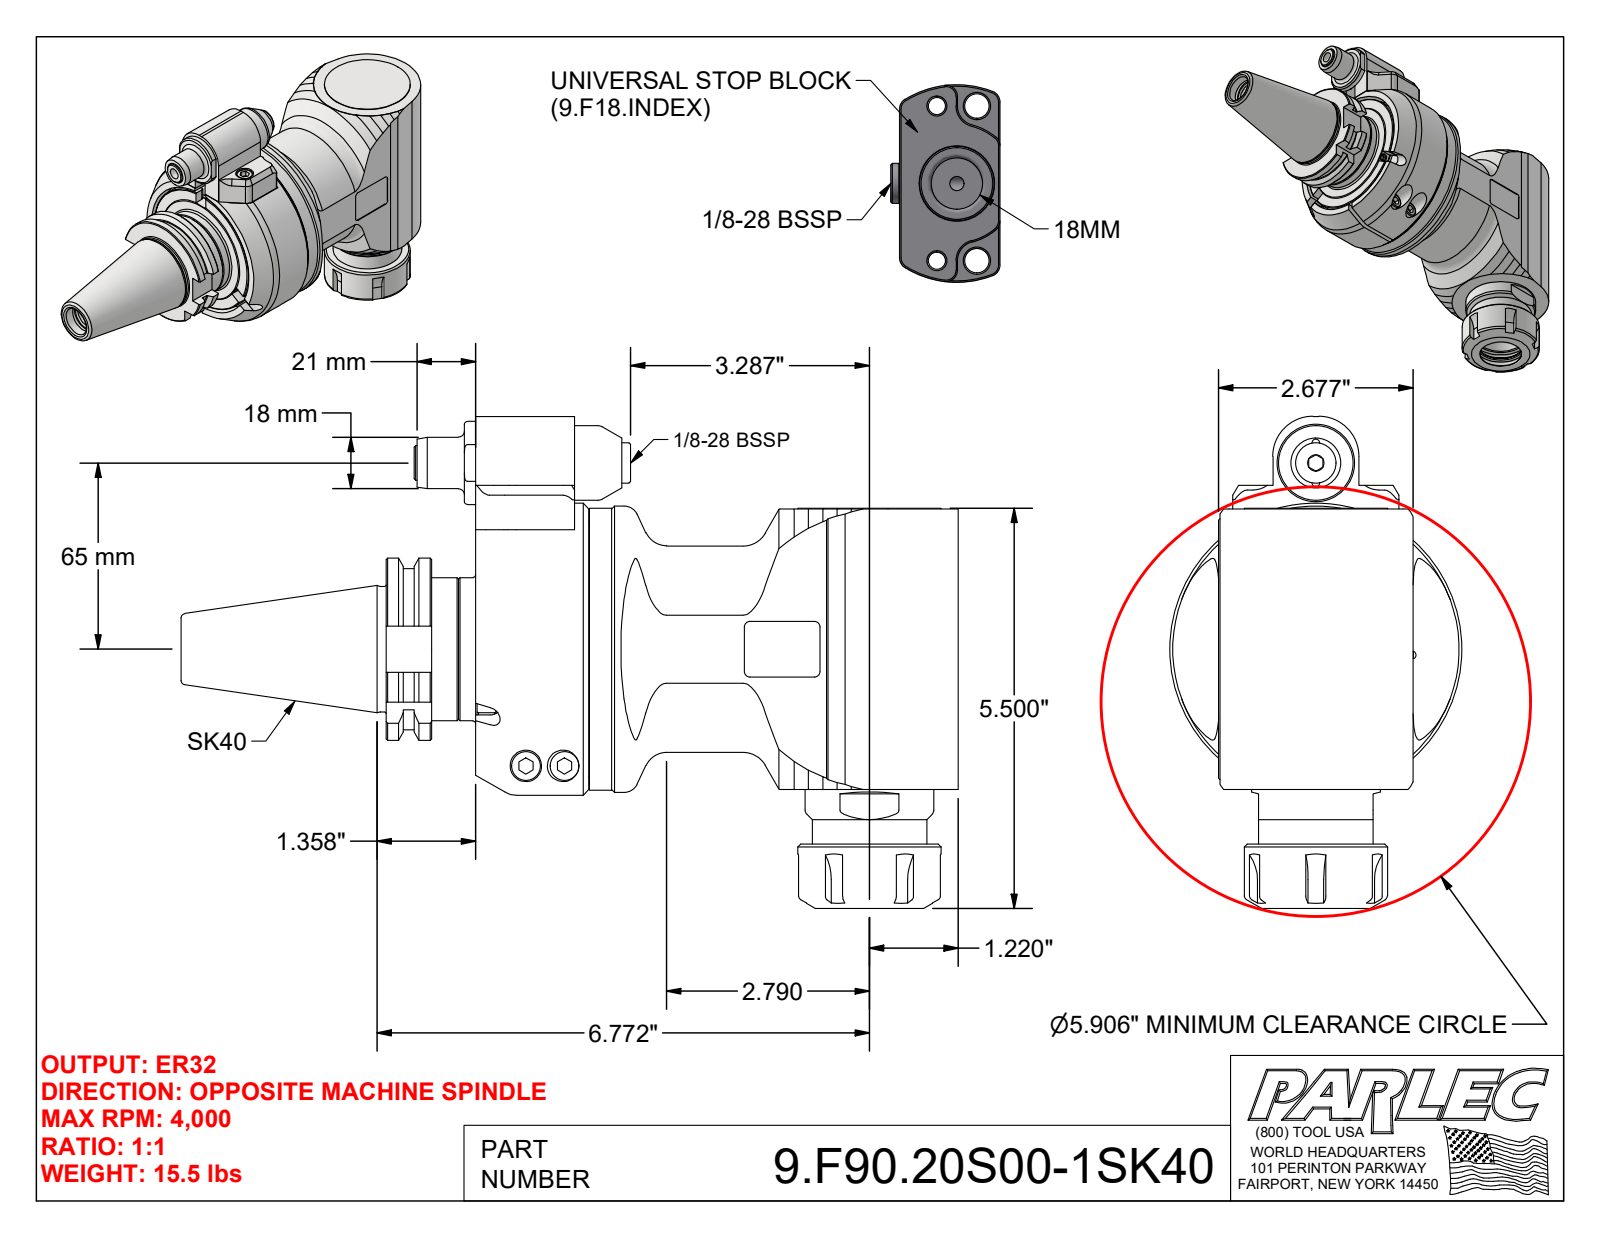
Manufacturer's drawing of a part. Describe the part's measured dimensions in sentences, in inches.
The part is named "9.F90.20S00-1SK40; 9_F90_20S00; 9_GA1_146_2 (Type 1, SK40, 65mm)". Its 3-D file was written by "Autodesk Inventor 2022 (AUTOMOTIVE_DESIGN)". It is 8 solids with 556 faces: 260 planar, 122 cylindrical and 174 other. Overall it measures 10.685 by 6.762 by 4.016 inches. Its volume is 73.5 cubic inches and its surface area 254.4 square inches. Round holes: 2 of diameter 0.102, 2 of diameter 0.165, 2 of diameter 0.197, 2 of diameter 0.409, 2 of diameter 0.433, 2 of diameter 0.492, 2 of diameter 1.063, 1 of diameter 0.098, 1 of diameter 0.118, 1 of diameter 0.256, 1 of diameter 0.276, 1 of diameter 0.472. Round bosses or shafts: 4 of diameter 0.394, 4 of diameter 0.236, 2 of diameter 1.969, 2 of diameter 0.709, 2 of diameter 0.098, 1 of diameter 4.016, 1 of diameter 3.937, 1 of diameter 3.874. Partial cylindrical surfaces (rounded edges, fillets, slot ends): 12 of radius 0.079, 6 of radius 0.591, 4 of radius 0.157, 2 of radius 0.02, 2 of radius 0.039, 2 of radius 0.138, 2 of radius 0.197, 2 of radius 0.236. The main face-to-face distances are 1.26, 0.02, 0.285, 0.276, 1.28, 1.555, 0.197, 0.295, 0.335, 2.677. The hole center spacings are 0.276, 0.512, 0.551, 1.72, 2.283, 2.559, 2.835, 4.138.
